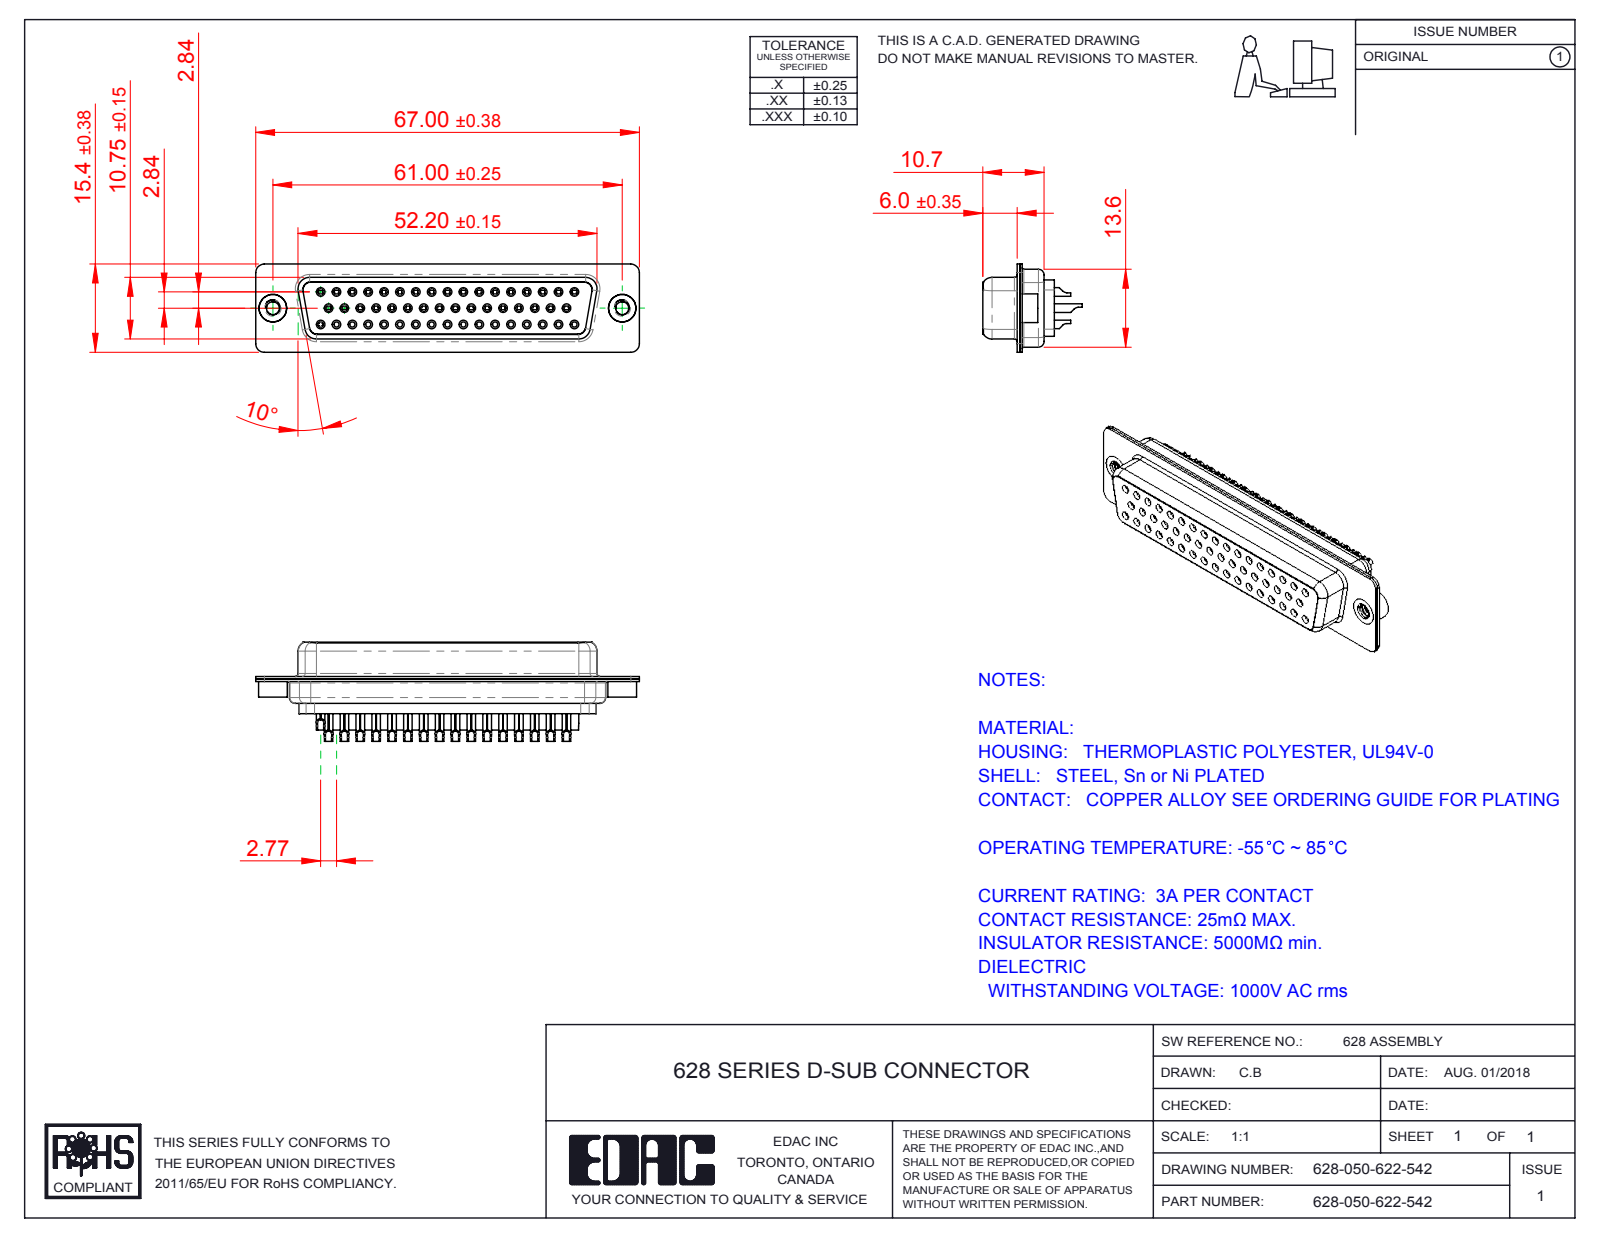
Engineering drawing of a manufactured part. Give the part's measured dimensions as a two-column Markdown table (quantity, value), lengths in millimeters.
| quantity | value |
| --- | --- |
| part name | 628 Housing_50 LP; 628 Shell Front_50 Contacts; 628 Shell Rear_50 Contacts; 628 Contact Row 1_22L (+4 more) |
| STEP written by | SolidWorks 2016 (CONFIG_CONTROL_DESIGN) |
| units | millimeters |
| bodies | 39 solids, 3513 faces (829 planar, 1115 cylindrical, 1569 other) |
| overall size | 67 × 17.35 × 15.4 |
| volume | 6 636 mm³ |
| surface area | 14 132 mm² |
| round holes (diameter × count) | 0.9 × 50, 1.6 × 50, 0.8 × 34, 1.1 × 34, 1.7 × 17, 1.5 × 16, 2 × 16, 2.26 × 2, 4 × 2, 4.8 × 2 |
| round bosses / shafts (diameter × count) | 2 × 34, 1.5 × 34, 1.2 × 34, 5 × 2, 4.9 × 2 |
| partial cylindrical surfaces (radius × count) | 0.28 × 33, 1.5 × 16, 2 × 12, 1.35 × 8, 1 × 7, 0.25 × 4, 0.5 × 4, 0.6 × 4 |
| main face-to-face distances | 0.45, 0.4, 10.3, 0.9, 6.05, 6.5, 12.5, 6.45, 6, 11.33 |
| hole center spacings | 3.16, 2.77, 5.54, 8.31, 11.08, 13.85, 16.62, 19.39 |
